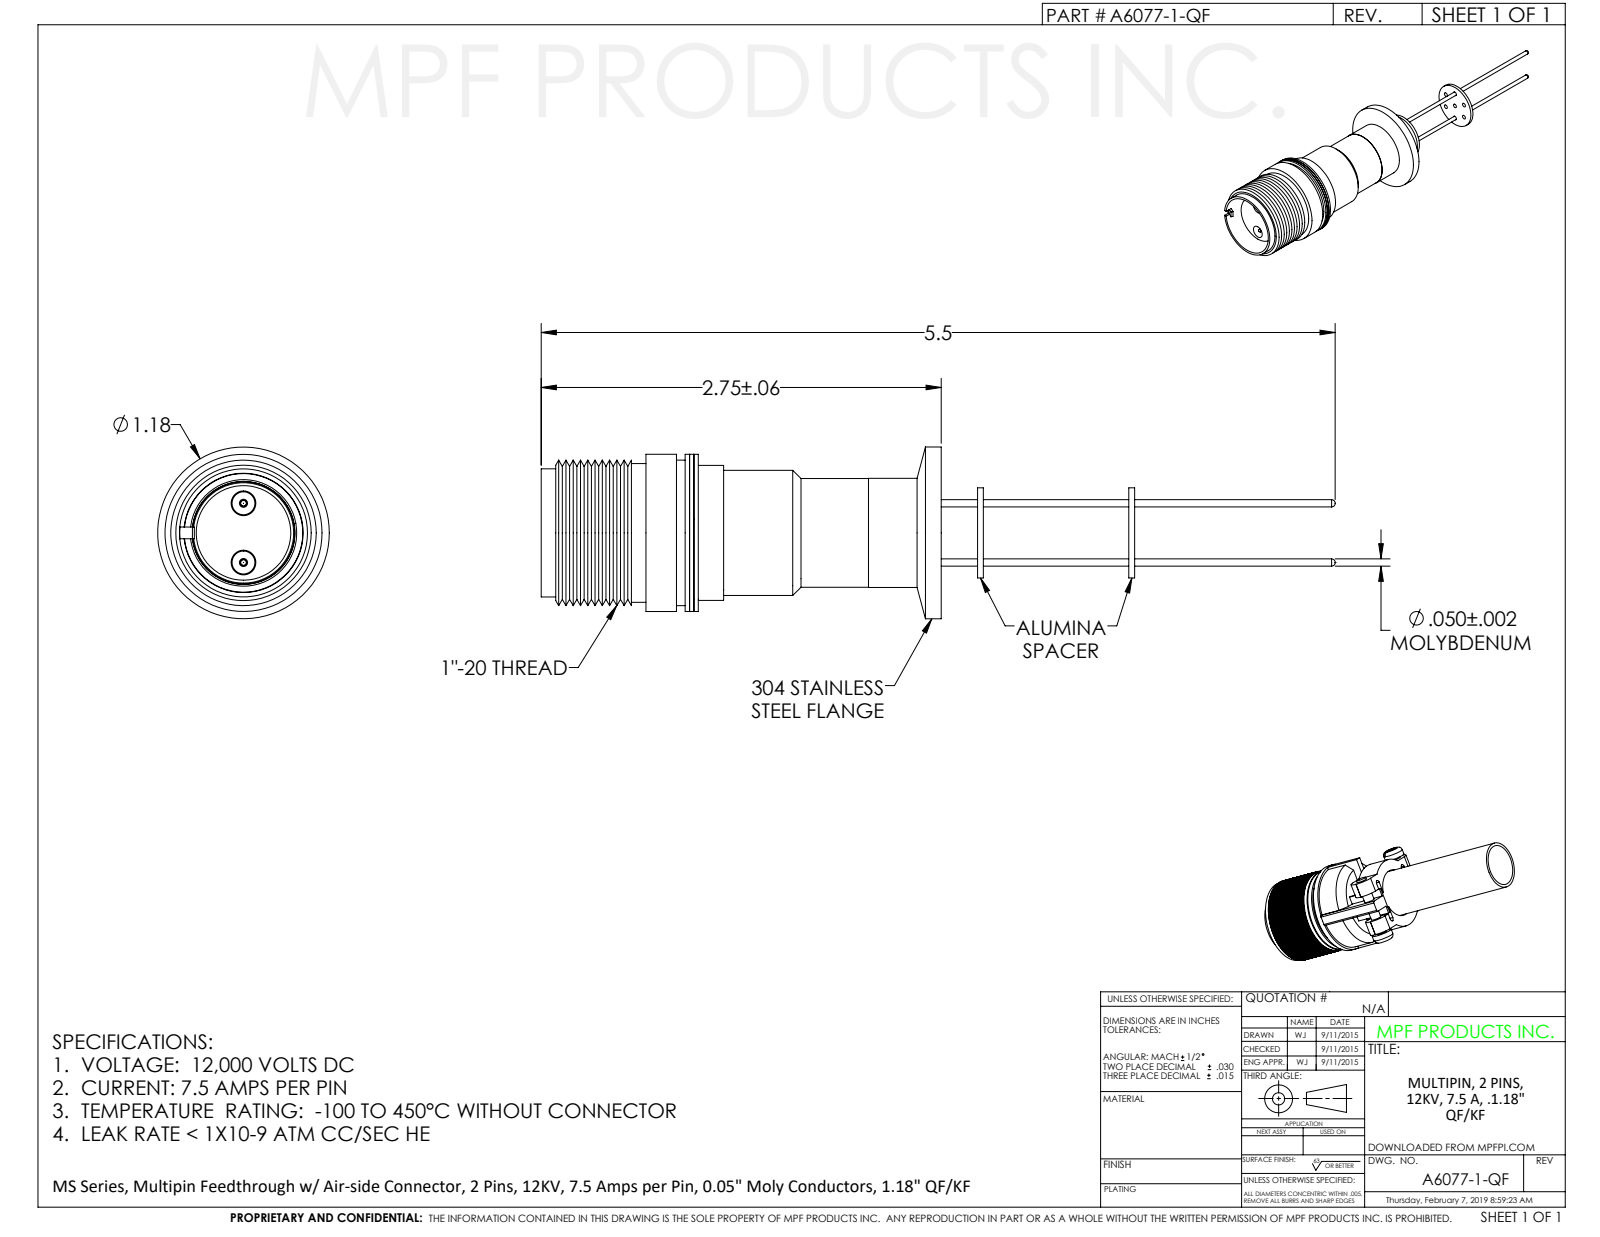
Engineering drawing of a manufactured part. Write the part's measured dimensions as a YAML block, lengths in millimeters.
part_name: "A6077-1-CF"
step_written_by: "SolidWorks 2011 (CONFIG_CONTROL_DESIGN)"
units: millimeters
bodies: {solids: 1, faces: 235, planar: 40, cylindrical: 105, other: 90}
overall_size: [138.8, 30, 30]
volume: 17760
surface_area: 17580
round_holes:
  - {diameter: 0.9, count: 5}
  - {diameter: 1.4, count: 2}
  - {diameter: 1.4, count: 2}
  - {diameter: 3.9, count: 2}
  - {diameter: 15.9, count: 1}
  - {diameter: 17.3, count: 1}
  - {diameter: 17.4, count: 1}
  - {diameter: 20.1, count: 1}
  - {diameter: 20.3, count: 1}
  - {diameter: 20.8, count: 1}
round_bosses_or_shafts:
  - {diameter: 3, count: 2}
  - {diameter: 1.3, count: 2}
  - {diameter: 1, count: 2}
  - {diameter: 30, count: 1}
  - {diameter: 27.4, count: 1}
  - {diameter: 25.4, count: 1}
  - {diameter: 24.2, count: 1}
  - {diameter: 23.6, count: 1}
face_to_face_distances: [26.5, 33.7, 7.2, 48.5, 22, 14.8, 34.7, 8.2, 1, 13.7]
hole_center_spacings: [5.2, 8.9, 10.3, 5.2, 9]
